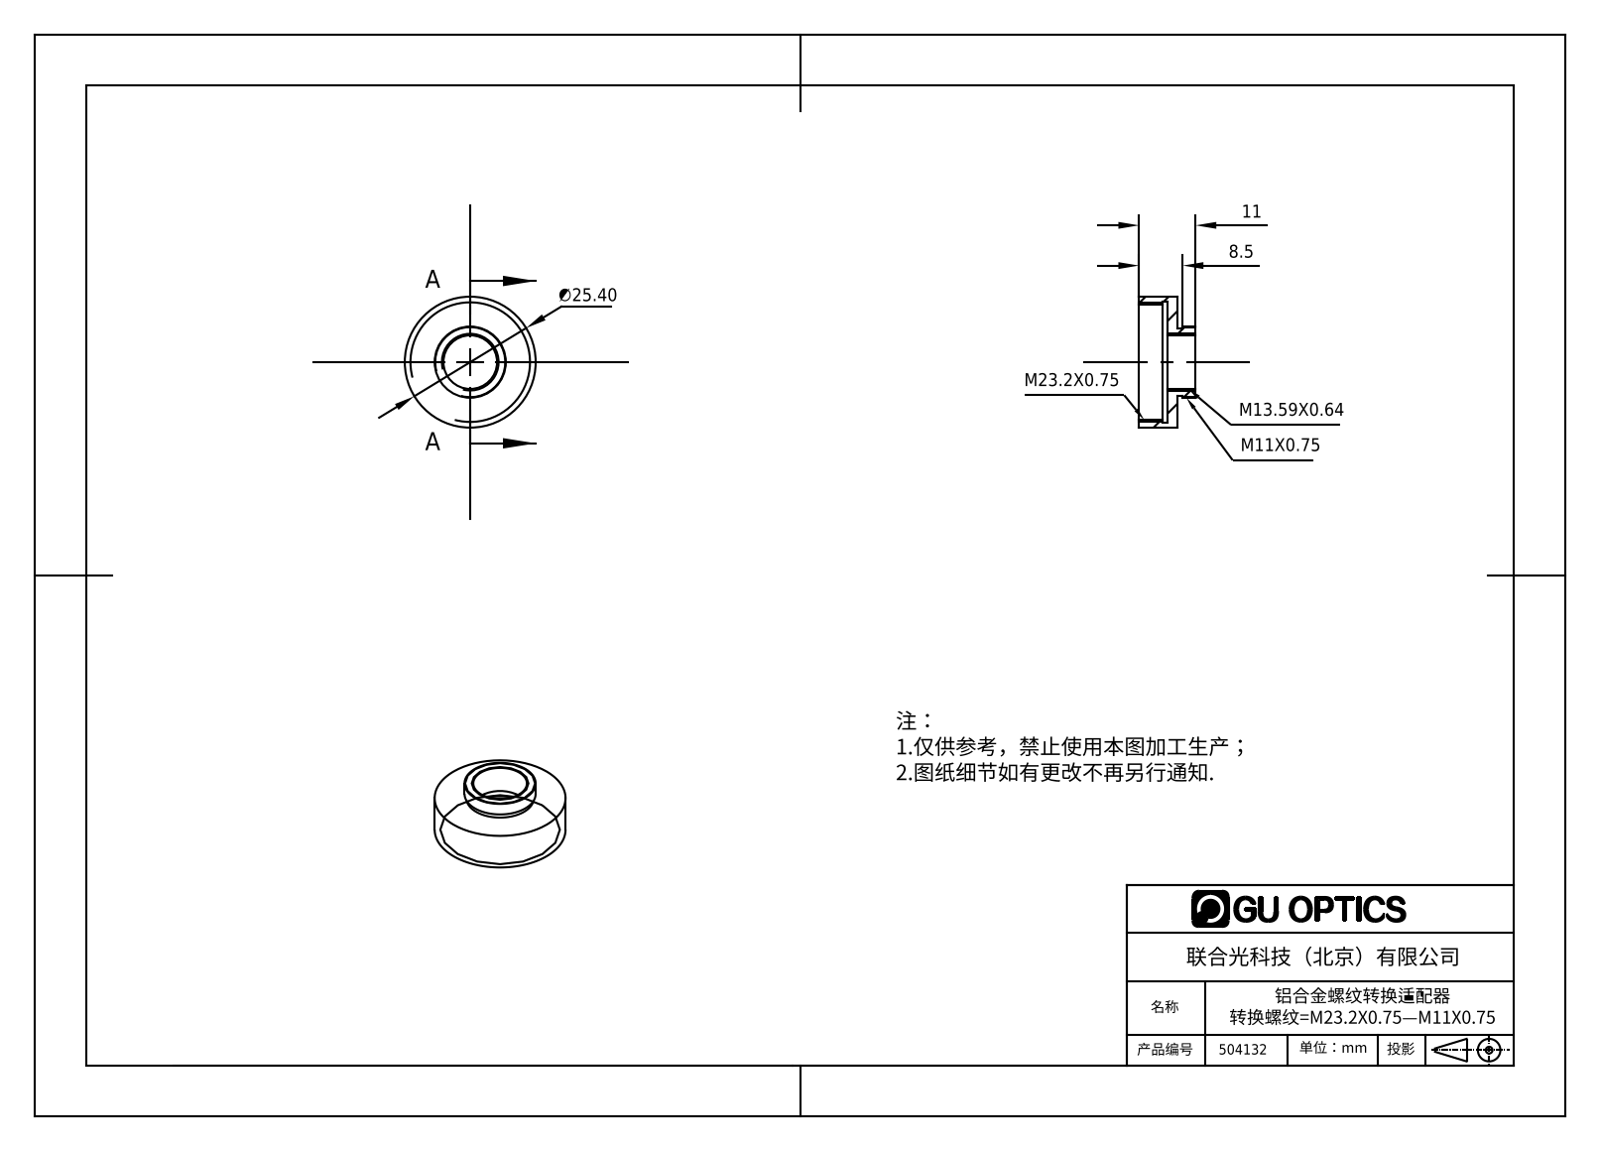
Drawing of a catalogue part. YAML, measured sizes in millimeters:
part_name: "504132"
step_written_by: "SolidWorks 2016 (AUTOMOTIVE_DESIGN)"
units: millimeters
bodies: {solids: 1, faces: 18, planar: 6, cylindrical: 12, other: 0}
overall_size: [25.4, 25.4, 11]
volume: 1638
surface_area: 2263
round_holes:
  - {diameter: 10.4, count: 1}
  - {diameter: 22.4, count: 1}
  - {diameter: 23.4, count: 1}
round_bosses_or_shafts:
  - {diameter: 25.4, count: 1}
  - {diameter: 13.8, count: 1}
  - {diameter: 13.1, count: 1}
face_to_face_distances: [2, 5.5, 7.5, 11, 3.5, 1, 3, 4.5, 6.5, 8.5]
